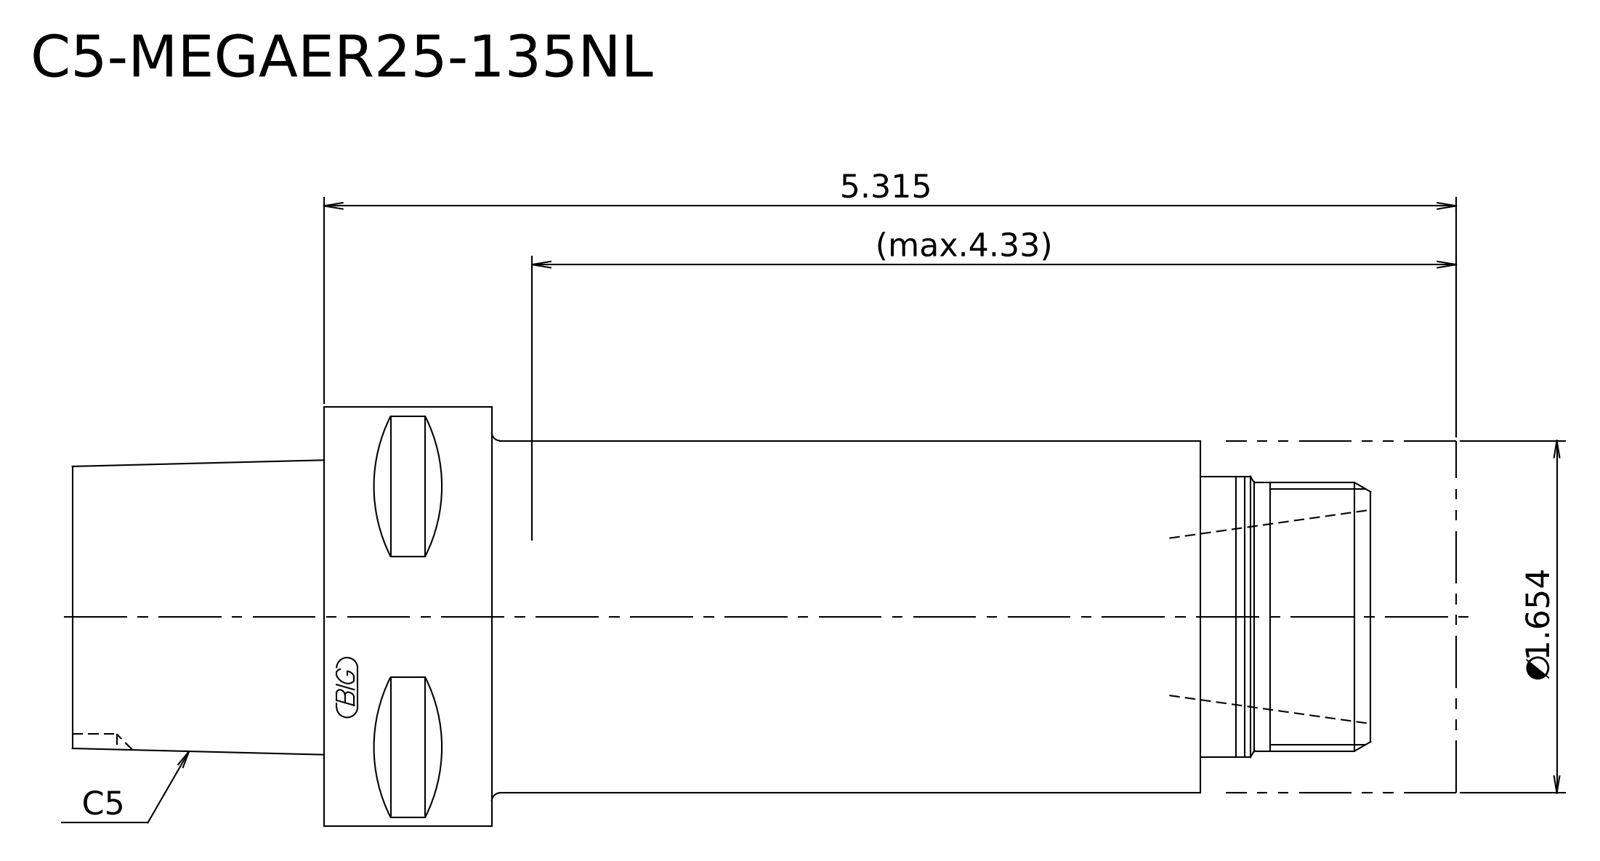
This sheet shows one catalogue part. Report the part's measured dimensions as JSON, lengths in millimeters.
{"step_written_by": "Kubotek KeyCreator 2011 V10.0.2 (22737) (automotive_design)", "units": "millimeters", "bodies": {"solids": 2, "faces": 16, "planar": 7, "cylindrical": 5, "other": 4}, "overall_size": [165, 50, 50], "volume_mm3": 238396, "surface_area_mm2": 29655, "round_bosses_or_shafts": [[50, 1], [42, 1], [33.5, 1], [32, 1]], "face_to_face_distances": [27.5, 135, 107.5, 165, 137.5, 30, 10.2, 17.3, 124.8, 154.8]}
